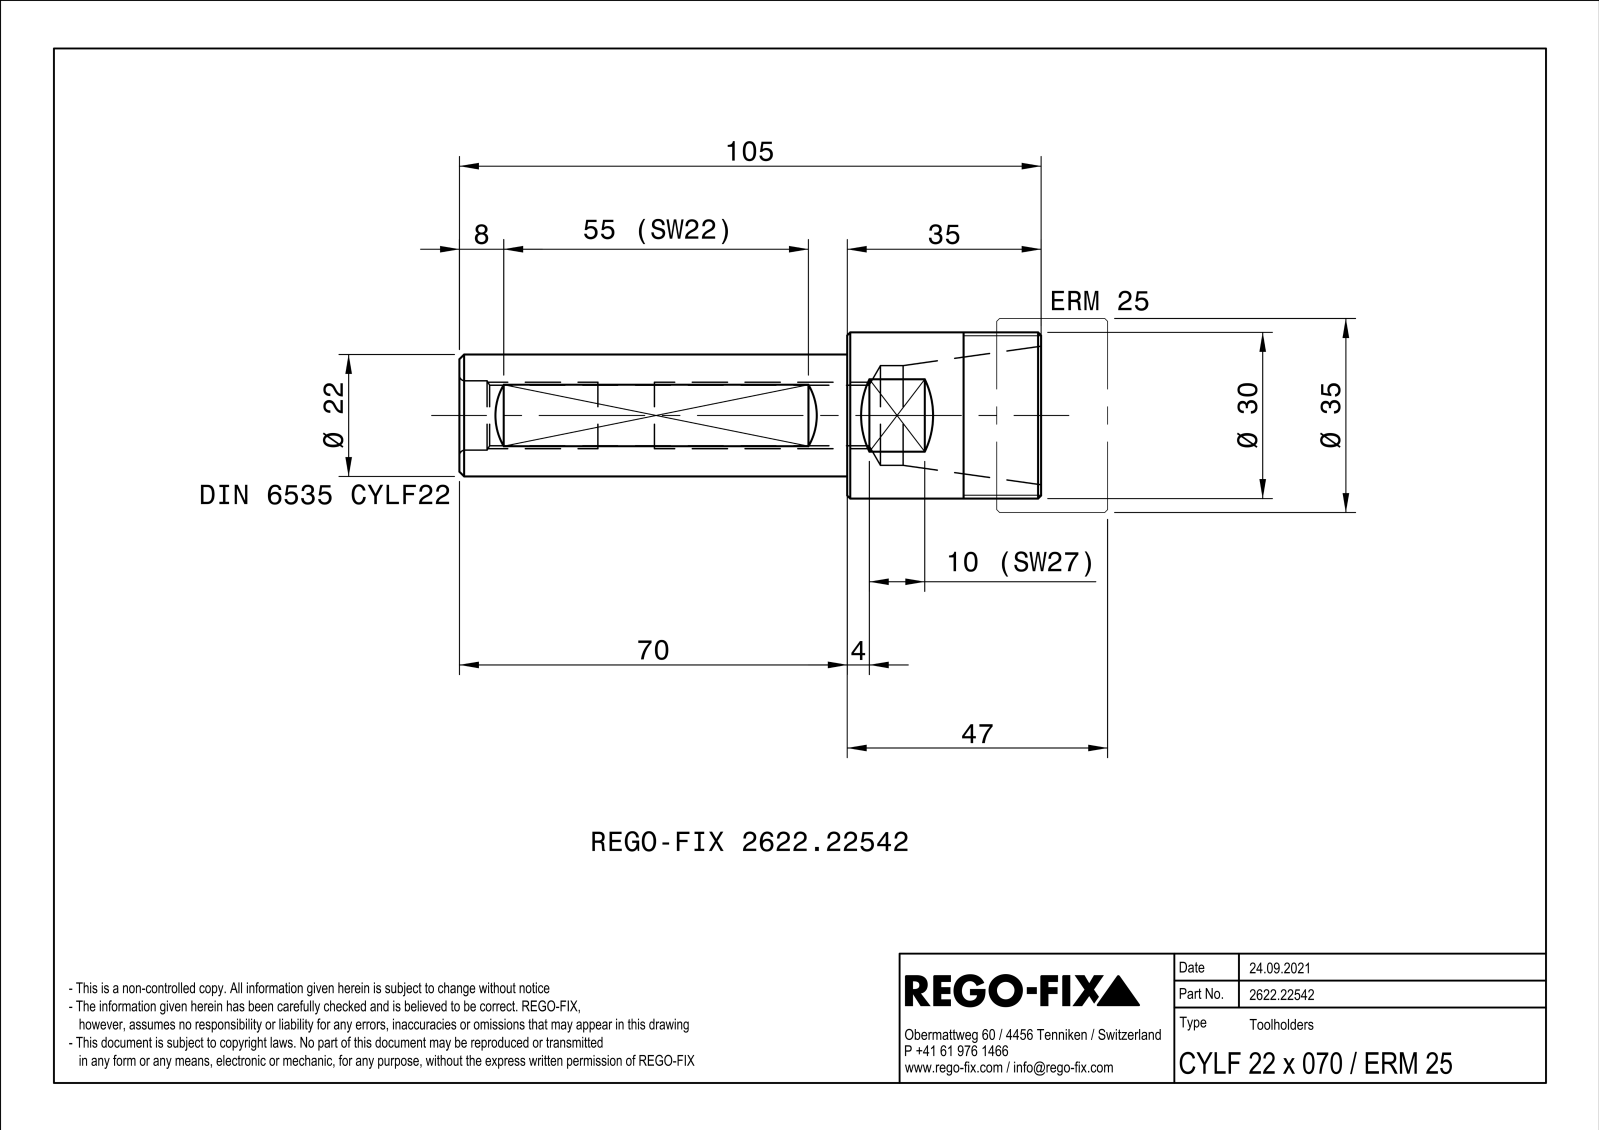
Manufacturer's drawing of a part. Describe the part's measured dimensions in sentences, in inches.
The part is named "NOCUT". Its 3-D file was written by "SIEMENS PLM Software Solid Edge ST10 (AUTOMOTIVE_DESIGN)". It is 1 solid with 31 faces: 12 planar, 9 cylindrical and 10 other. Overall it measures 4.134 by 1.181 by 1.181 inches. Its volume is 2 cubic inches and its surface area 20.92 square inches. Round holes: 1 of diameter 0.43, 1 of diameter 0.492, 1 of diameter 0.709. Round bosses or shafts: 1 of diameter 1.181, 1 of diameter 0.866, 1 of diameter 0.85. The main face-to-face distances are 2.756, 1.378, 4.134, 0.906, 1.063, 0.157, 0.473, 1.475, 1.948, 0.946.
